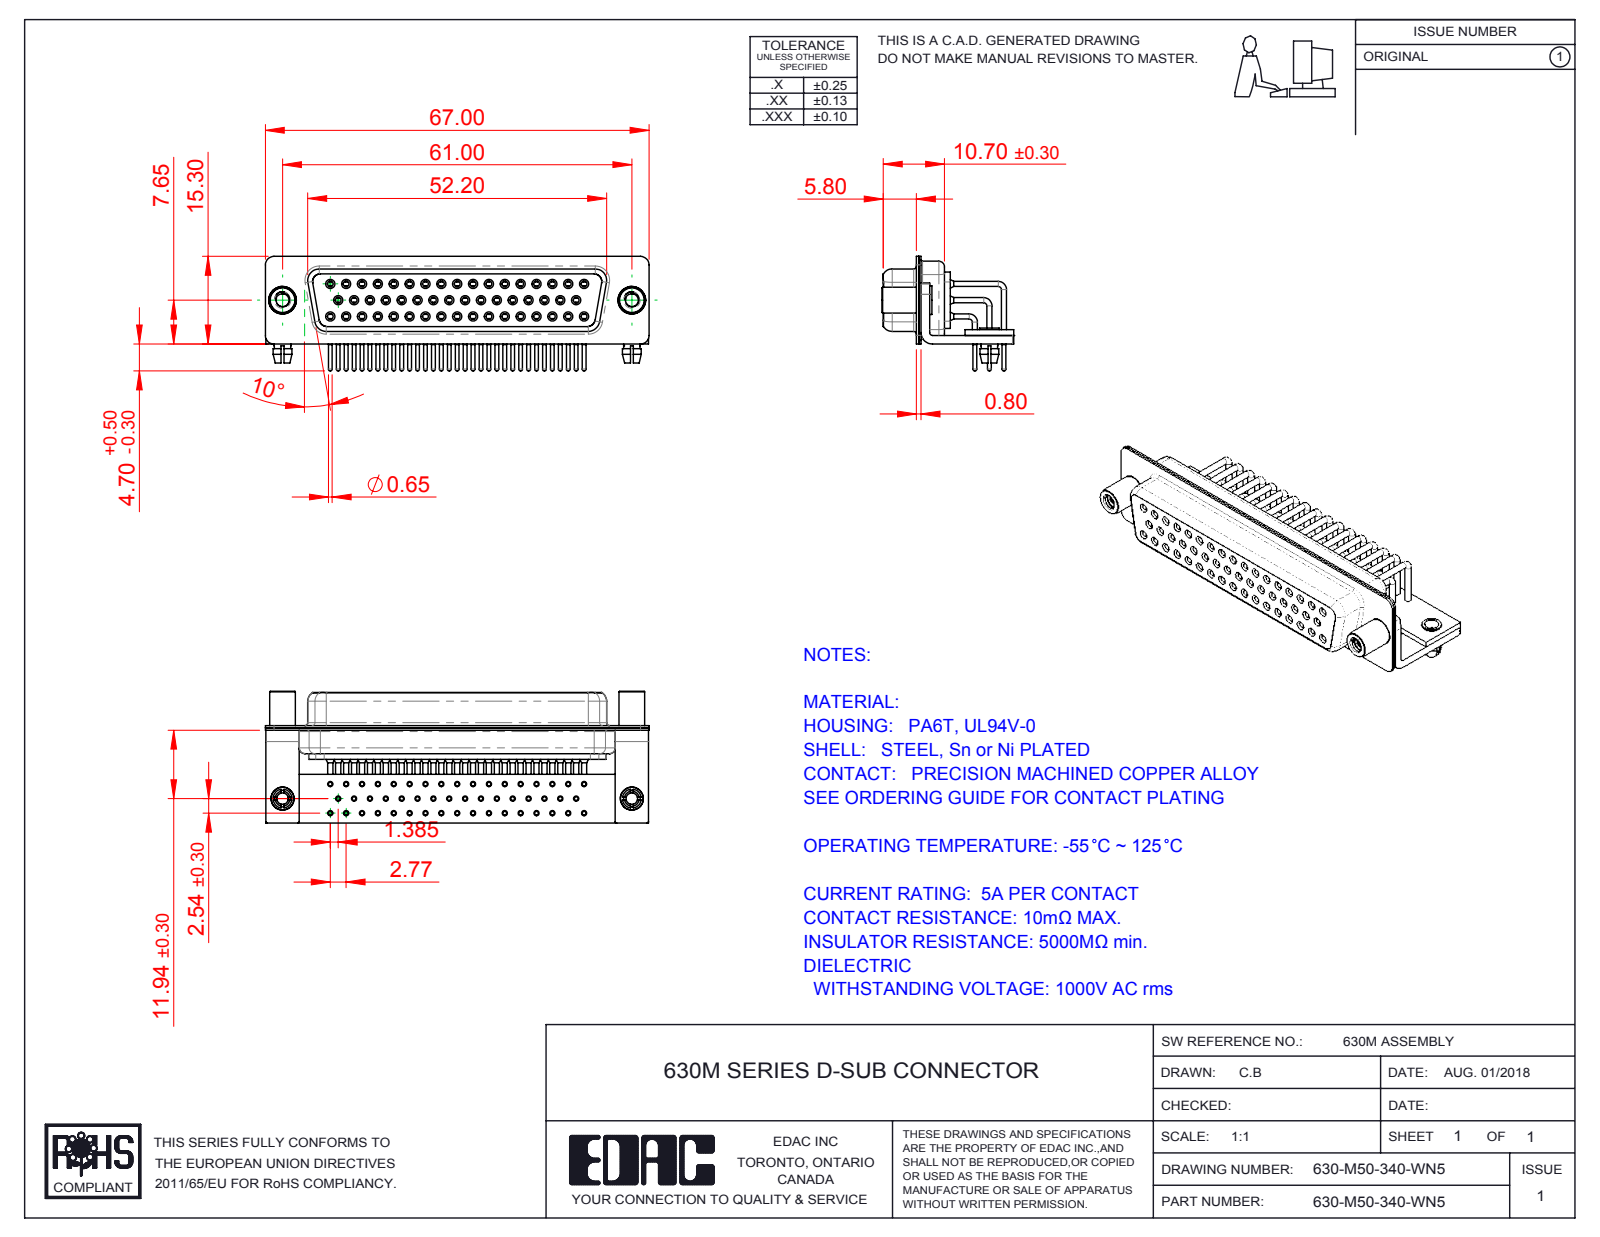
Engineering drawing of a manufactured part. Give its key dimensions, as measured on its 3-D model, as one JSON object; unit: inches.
{"part_name": "630M Board Lock_50 Contacts; 630M Stabilizer Bracket_50 Contacts; 630M 4-40 Threaded Standoff; 630M Shell Rear_50 Contacts (+7 more)", "step_written_by": "SolidWorks 2016 (CONFIG_CONTROL_DESIGN)", "units": "inches", "bodies": {"solids": 60, "faces": 3221, "planar": 893, "cylindrical": 1483, "other": 845}, "overall_size": [2.638, 0.906, 0.787], "volume_in3": 0.49, "surface_area_in2": 29.71, "round_holes": [[0.079, 52], [0.035, 50], [0.039, 50], [0.043, 50], [0.067, 50], [0.071, 50], [0.089, 2], [0.098, 2], [0.126, 2], [0.157, 2], [0.189, 2]], "round_bosses_or_shafts": [[0.035, 59], [0.063, 50], [0.059, 50], [0.026, 50], [0.197, 2], [0.193, 2], [0.177, 2], [0.157, 2]], "partial_cylinders_radius": [[0.01, 16], [0.059, 16], [0.079, 13], [0.053, 8], [0.063, 8], [0.02, 5], [0.024, 4], [0.026, 4]], "face_to_face_distances": [0.016, 0.039, 0.087, 0.033, 0.053, 0.467, 0.482, 0.228, 0.031, 0.232], "hole_center_spacings": [0.109, 0.218, 0.327, 0.436, 0.545, 0.654, 0.124, 0.763]}
